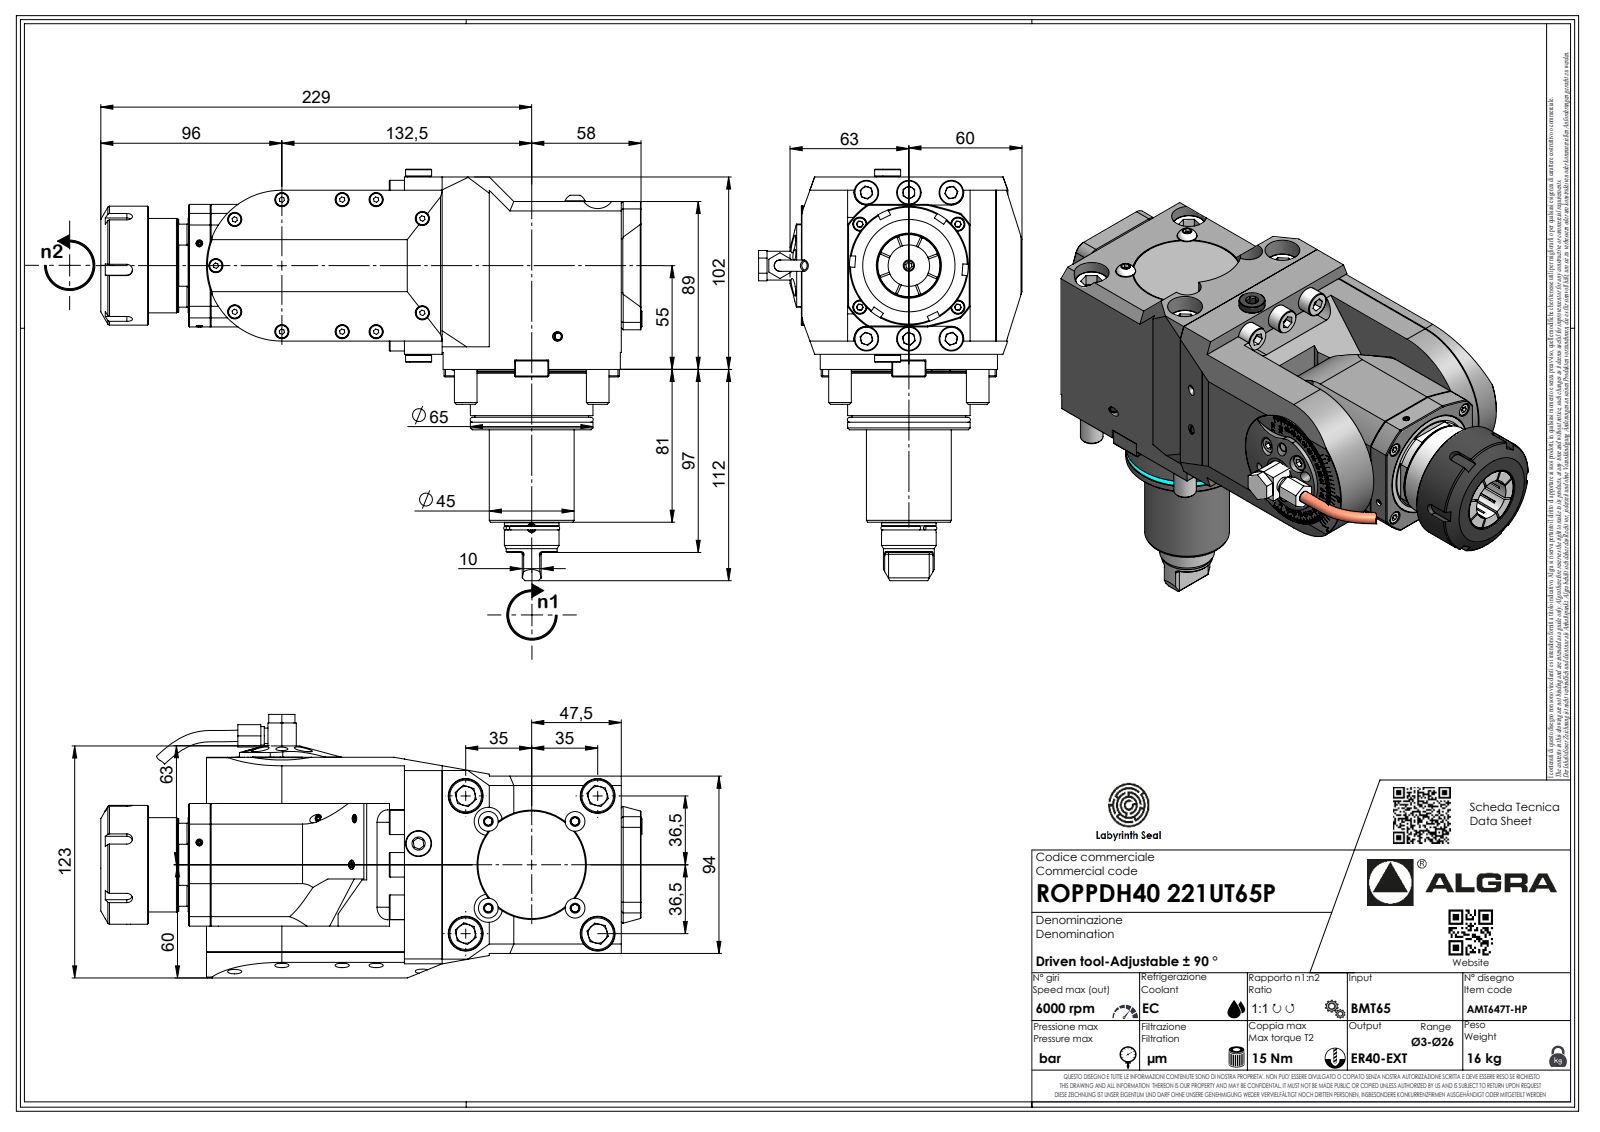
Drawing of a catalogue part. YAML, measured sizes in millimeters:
part_name: "ROPPDH40221UT65P"
step_written_by: "SolidWorks 2023 (AUTOMOTIVE_DESIGN)"
units: millimeters
bodies: {solids: 1, faces: 832, planar: 535, cylindrical: 134, other: 163}
overall_size: [286.52, 218.15, 139.7]
volume: 2226000
surface_area: 161636
round_holes:
  - {diameter: 4, count: 2}
  - {diameter: 2.1, count: 1}
  - {diameter: 3.3, count: 1}
  - {diameter: 17, count: 1}
round_bosses_or_shafts:
  - {diameter: 13, count: 6}
  - {diameter: 12, count: 5}
  - {diameter: 10.5, count: 2}
  - {diameter: 65, count: 1}
  - {diameter: 64.6, count: 1}
  - {diameter: 63, count: 1}
  - {diameter: 60.3, count: 1}
  - {diameter: 50, count: 1}
partial_cylinders:
  - {radius: 3, count: 13}
  - {radius: 0.33, count: 7}
  - {radius: 0.52, count: 7}
  - {radius: 3.7, count: 7}
  - {radius: 1, count: 6}
  - {radius: 6, count: 4}
  - {radius: 6.62, count: 4}
  - {radius: 10.5, count: 4}
face_to_face_distances: [14.5, 79.5, 94, 13, 65, 89, 102, 87, 7, 72.5]
hole_center_spacings: [39.15, 95.82]
